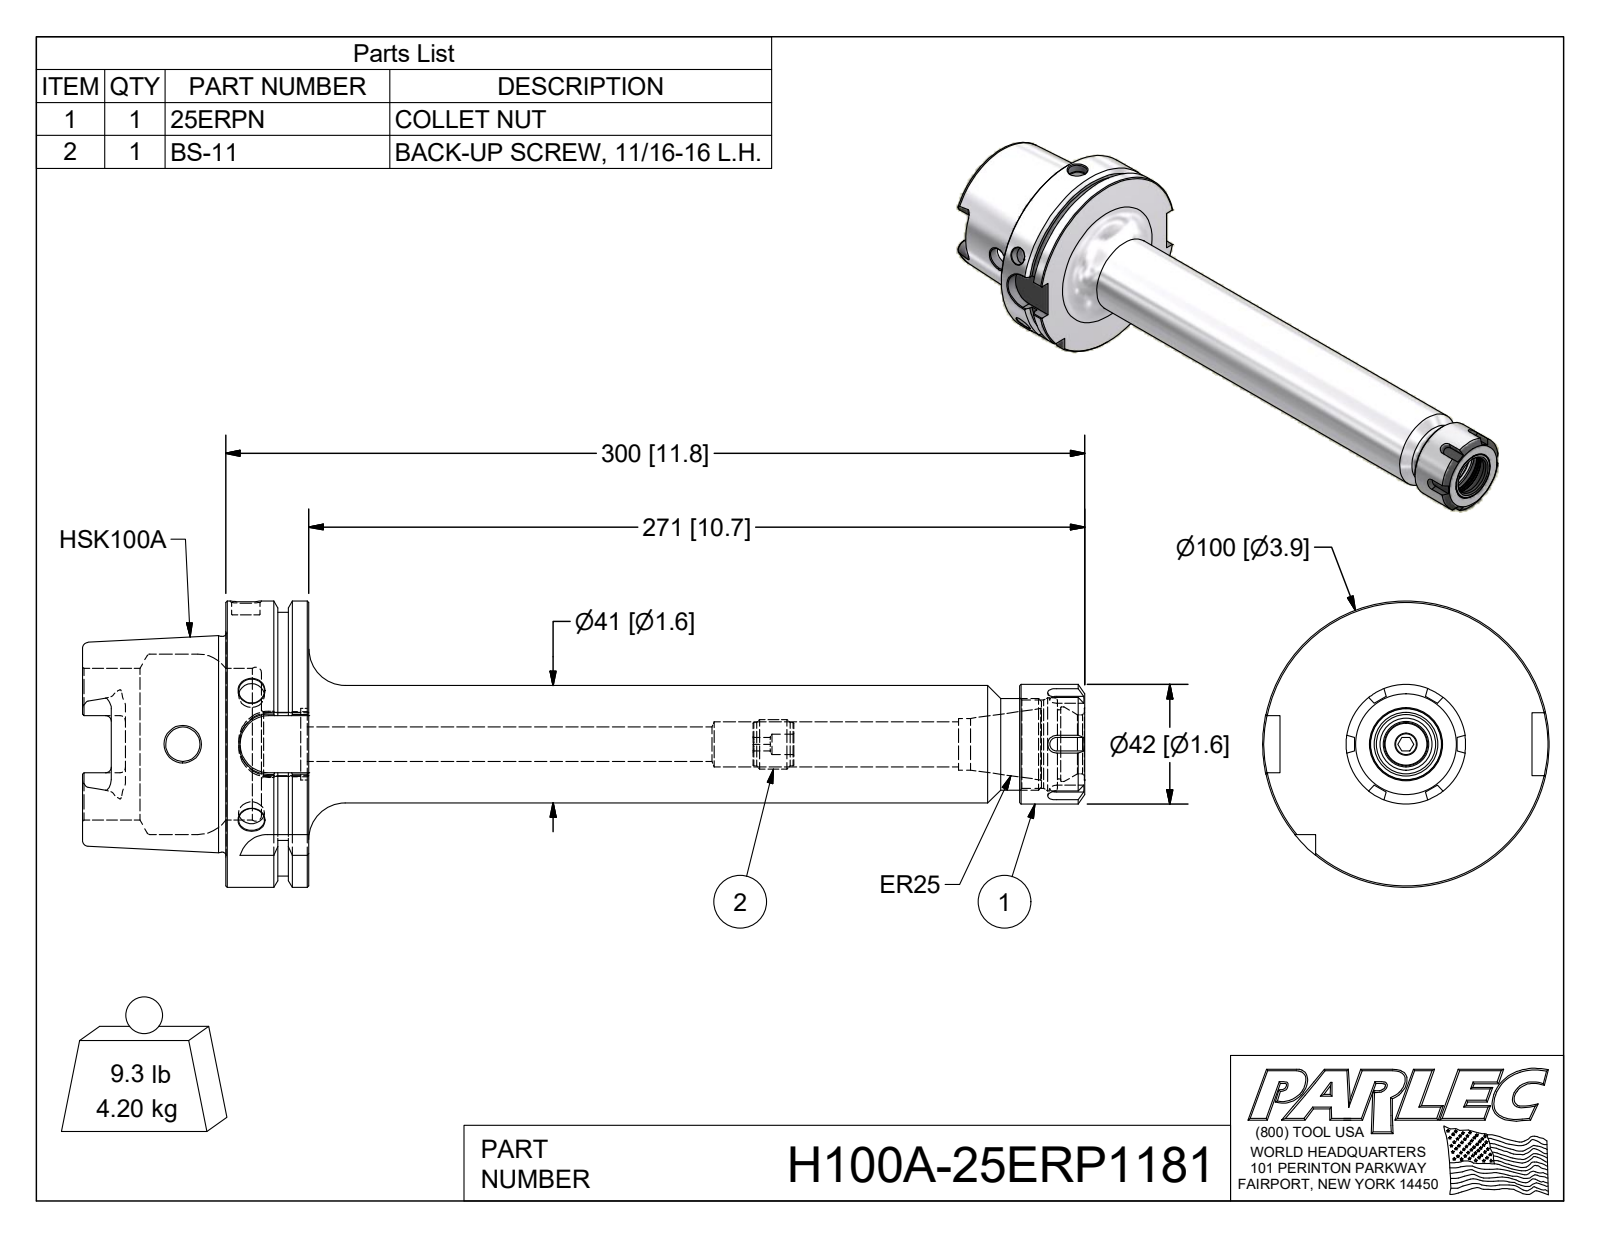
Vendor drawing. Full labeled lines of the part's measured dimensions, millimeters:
Part name (STEP PRODUCT): H100A-25ERP1181; 25ERPN; BS-11
STEP written by: Autodesk Inventor 2016 (AUTOMOTIVE_DESIGN)
Units: millimetres
Bodies: 3 solids, 199 faces (72 planar, 47 cylindrical, 80 other)
Overall size (bounding box): 349.97 × 100 × 100
Volume: 563 323 mm³ · Surface area: 100 982 mm²
Round holes (diameter × count): ⌀9 ×2, ⌀12 ×2, ⌀7.11 ×1, ⌀10 ×1, ⌀15.75 ×1, ⌀18.03 ×1, ⌀20.6 ×1, ⌀22.38 ×1, ⌀24.13 ×1, ⌀25.02 ×1, ⌀26.09 ×1, ⌀30.91 ×1
Round bosses / shafts (diameter × count): ⌀100 ×1, ⌀92 ×1, ⌀75.36 ×1, ⌀41.73 ×1, ⌀41 ×1, ⌀32 ×1, ⌀17.3 ×1, ⌀15.11 ×1
Partial cylindrical surfaces — rounded edges, fillets, slot ends (radius × count): R2 ×6, R4.88 ×4, R10 ×4
Main face-to-face distances: 29, 12.5, 16.5, 50, 62.5, 79, 349.97, 299.97, 287.47, 270.97
